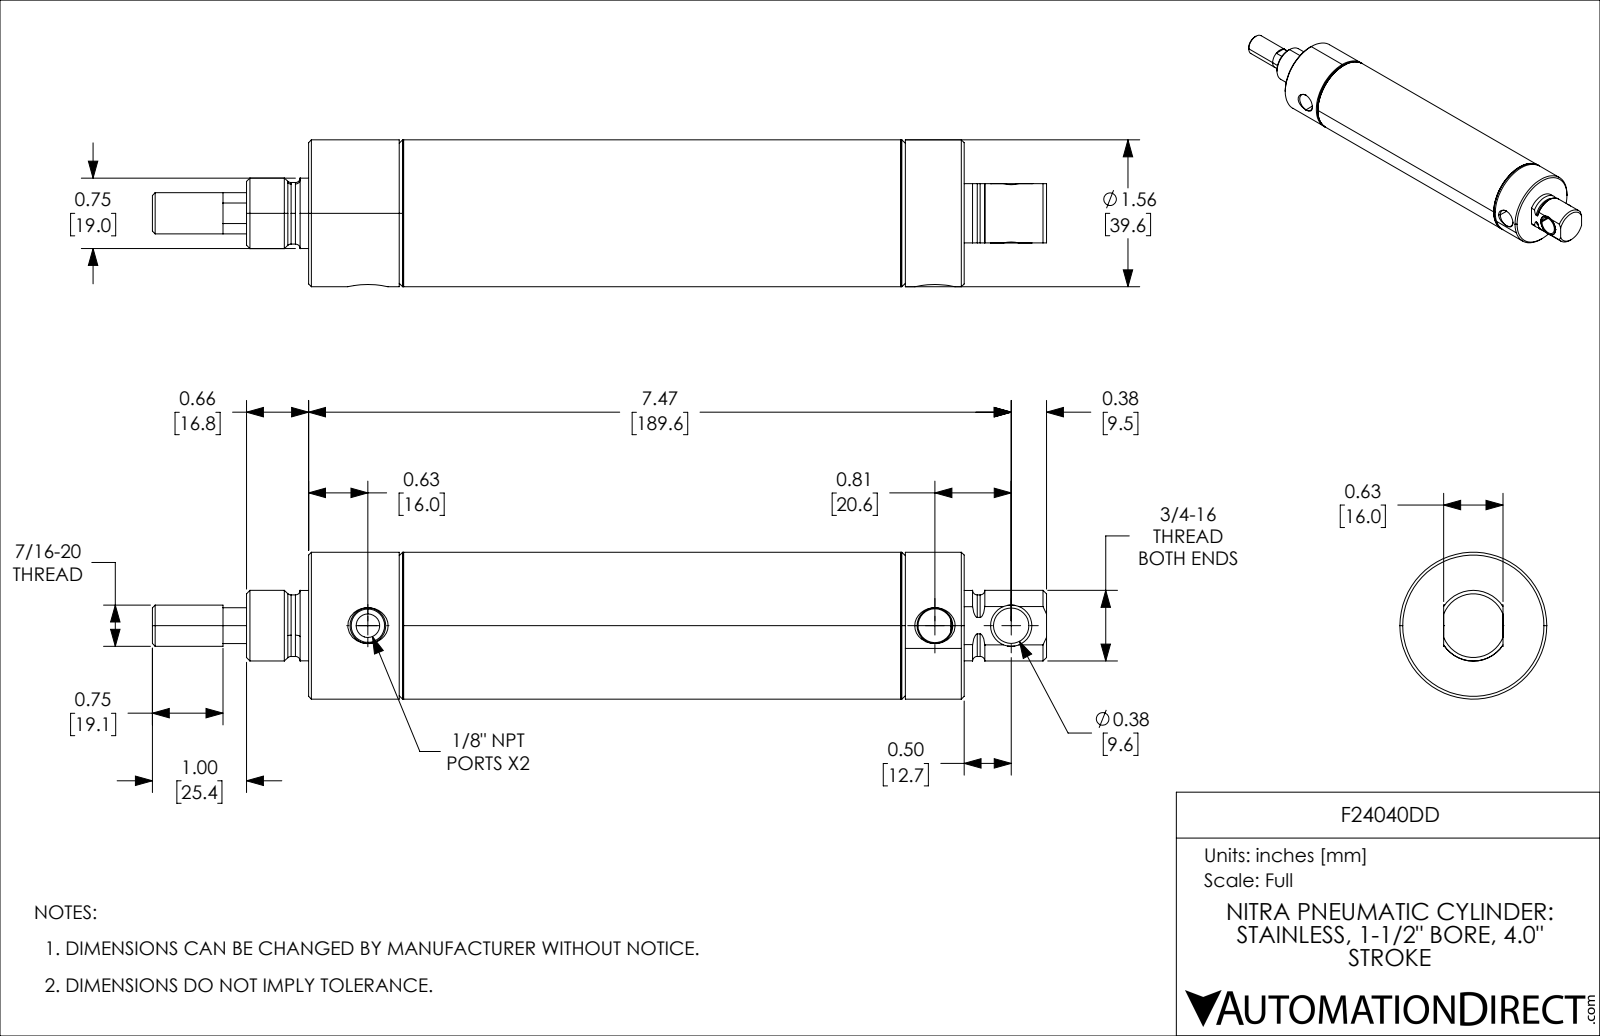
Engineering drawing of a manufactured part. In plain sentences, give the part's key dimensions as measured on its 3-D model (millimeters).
The part is named "F24040DD_5; F24040DD_7; F24040DD; F24040DD_3 (+2 more)". Its 3-D file was written by "SolidWorks 2021 (CONFIG_CONTROL_DESIGN)". It is 5 solids with 157 faces: 35 planar, 58 cylindrical and 64 other. Overall it measures 241.3 by 39.62 by 39.62 millimeters. Its volume is 113 158 cubic millimeters and its surface area 64 064 square millimeters. Round holes: 1 of diameter 6.35, 1 of diameter 9.14, 1 of diameter 9.55, 1 of diameter 11.15, 1 of diameter 11.73, 1 of diameter 13.51, 1 of diameter 26.97, 1 of diameter 36.36. Round bosses or shafts: 1 of diameter 39.62, 1 of diameter 38.39, 1 of diameter 19.05, 1 of diameter 18.99, 1 of diameter 16.61, 1 of diameter 16.6, 1 of diameter 11.13, 1 of diameter 11.11. The main face-to-face distances are 22.22, 44.45, 101.6, 123.82, 146.05, 22.23, 30.86, 132.46, 154.68, 176.91. The hole center spacings are 20.57, 153.04, 173.61.
